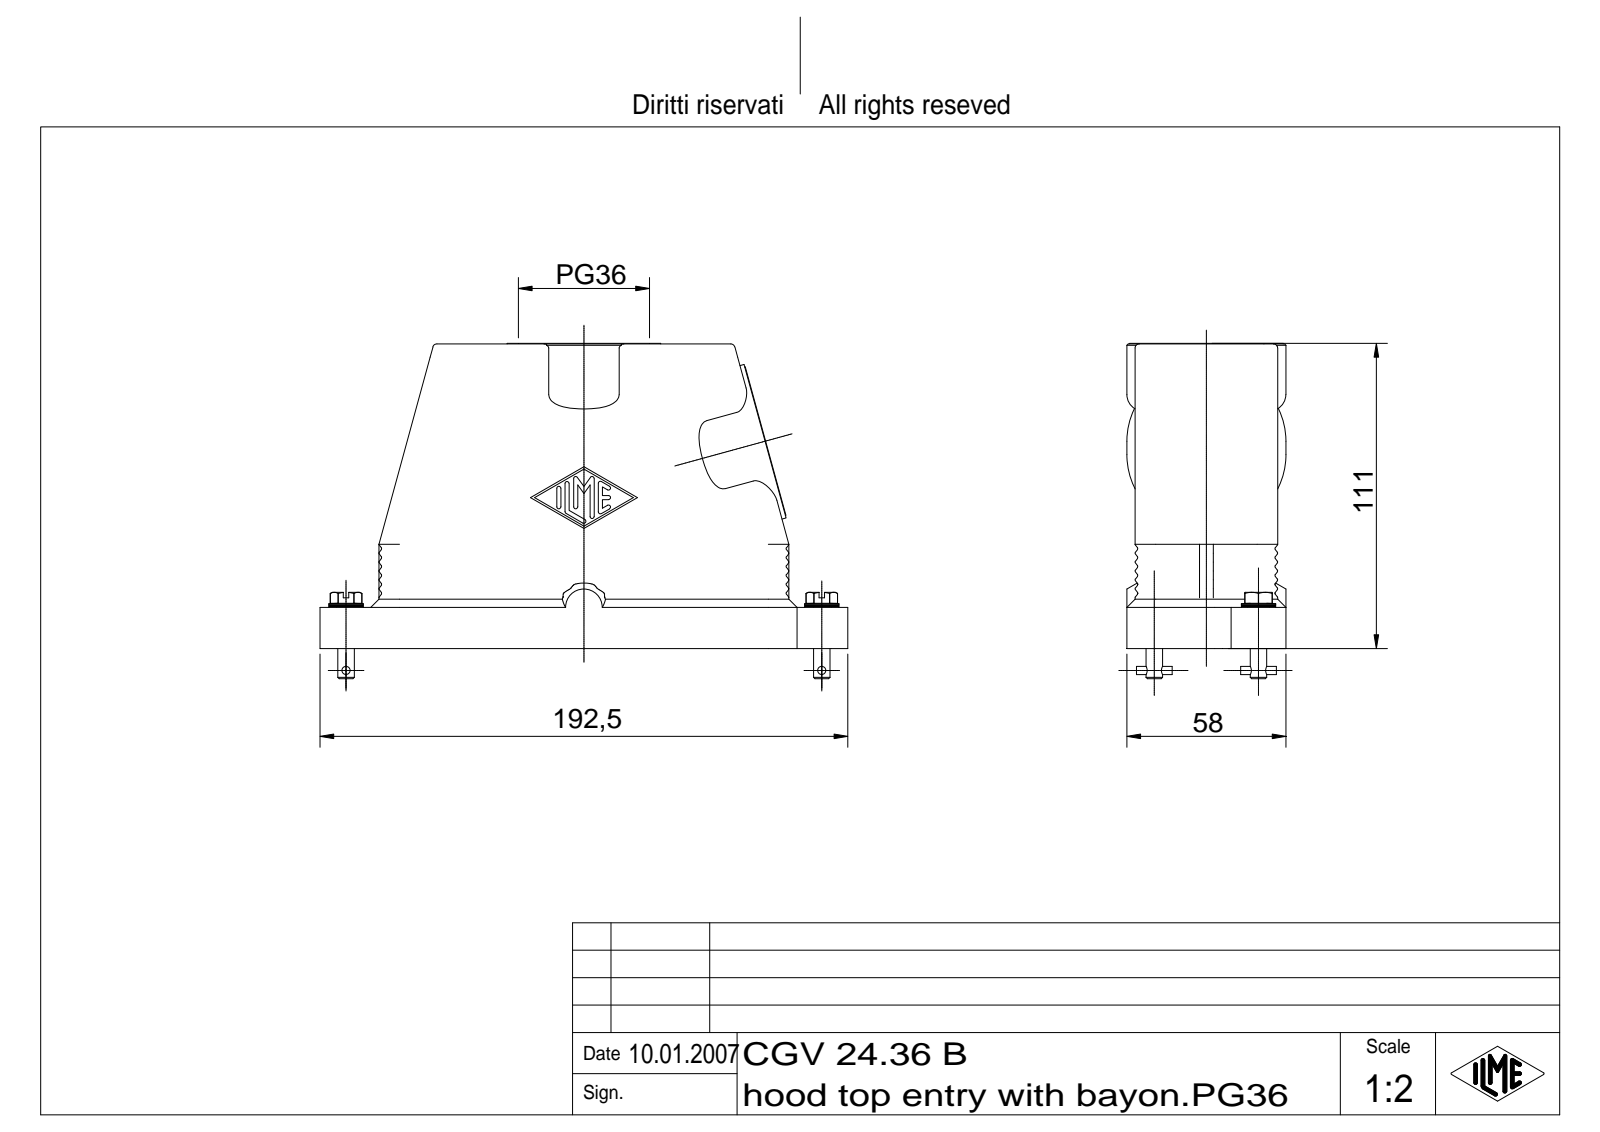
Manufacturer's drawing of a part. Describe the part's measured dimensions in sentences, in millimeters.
The part is named "CGV 24.36 B". Its 3-D file was written by "Autodesk Inventor 7 (AUTOMOTIVE_DESIGN)". It is 3 solids with 779 faces: 193 planar, 203 cylindrical and 383 other. Overall it measures 192.5 by 122.2 by 58 millimeters. Its volume is 236 218 cubic millimeters and its surface area 107 040 square millimeters. Round holes: 2 of diameter 2.46, 2 of diameter 3.2, 2 of diameter 6.6, 2 of diameter 15, 1 of diameter 45.48. Round bosses or shafts: 2 of diameter 58, 2 of diameter 56, 2 of diameter 12.5, 2 of diameter 6, 2 of diameter 3. Partial cylindrical surfaces (rounded edges, fillets, slot ends): 39 of radius 0.5, 14 of radius 0.75, 8 of radius 7.5, 6 of radius 6, 4 of radius 1.5, 4 of radius 3, 2 of radius 5.75, 2 of radius 10.5. The main face-to-face distances are 3, 52, 49, 46, 6, 55, 2.5, 0.5, 58, 3.5. The hole center spacings are 35.18, 142.51, 107.45, 177.61.
